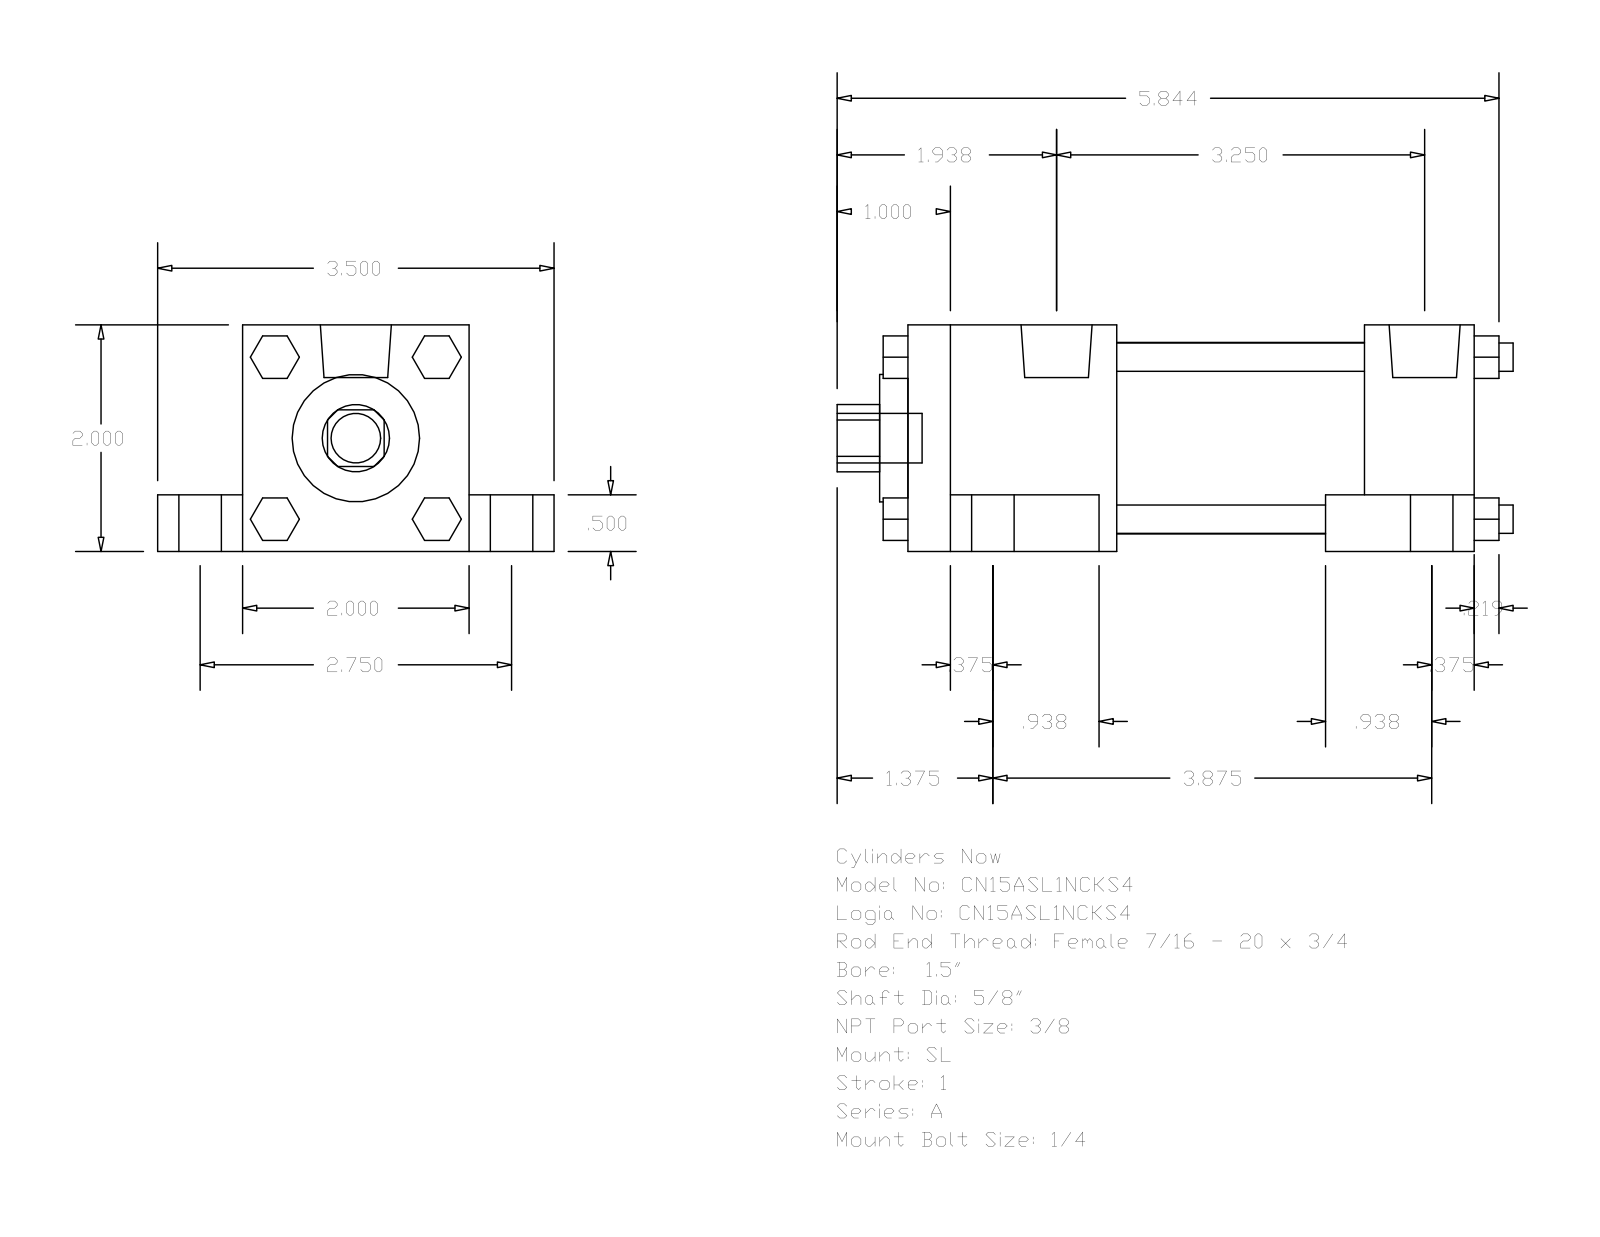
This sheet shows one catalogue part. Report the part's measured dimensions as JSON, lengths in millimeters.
{"part_name": "A_SL__0150_0.625", "step_written_by": "GSSL Pune (CONFIG_CONTROL_DESIGN)", "units": "millimeters", "bodies": {"solids": 0, "faces": 148, "planar": 112, "cylindrical": 36, "other": 0}, "overall_size": [151.61, 88.9, 50.8], "round_holes": [[15.88, 1], [28.57, 1], [42.93, 1]], "round_bosses_or_shafts": [[15.88, 4], [9.53, 4], [6.35, 4], [5.56, 4], [15.93, 2], [11.11, 1]], "partial_cylinders_radius": [[7.54, 1]], "face_to_face_distances": [50.8, 19.05, 12.7, 38.1, 69.85, 127, 9.52, 46.83, 33.34, 102.39]}
